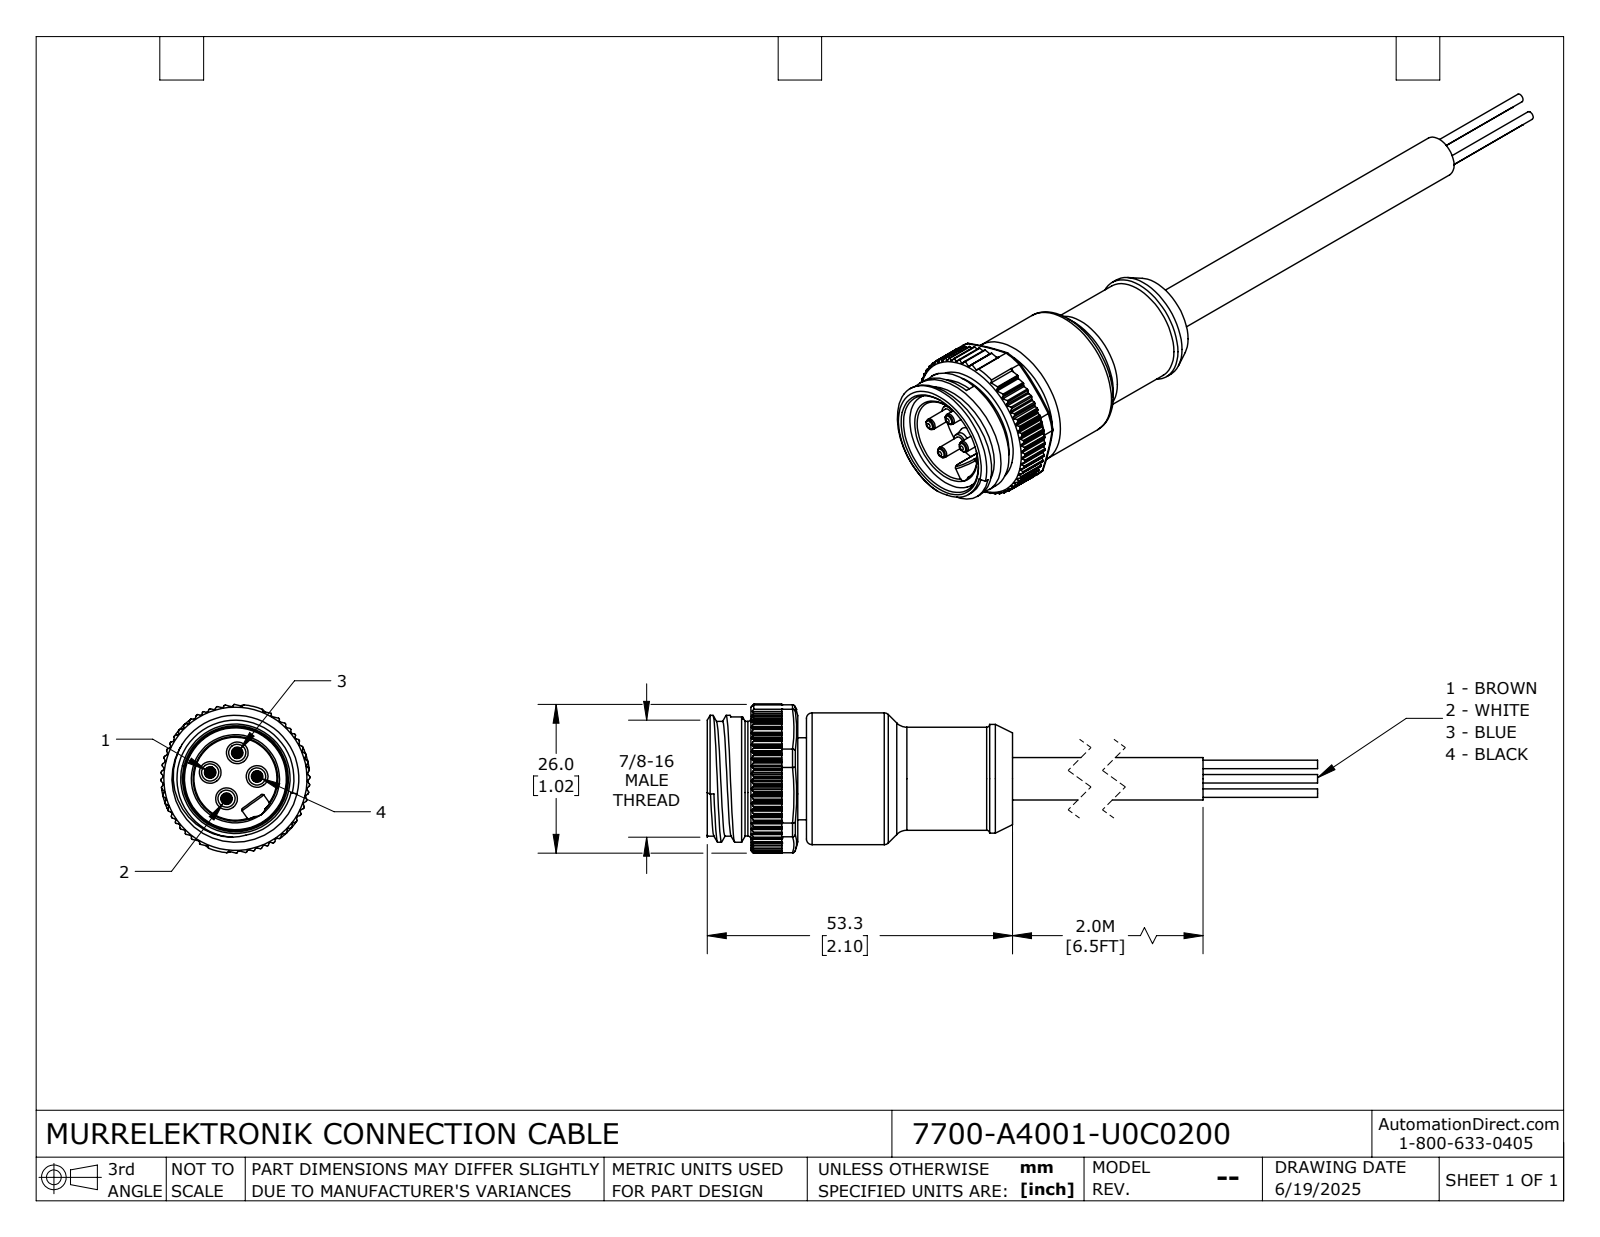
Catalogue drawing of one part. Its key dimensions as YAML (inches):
part_name: "7700-A4001-U0C0200"
step_written_by: "SolidWorks 2024 (CONFIG_CONTROL_DESIGN)"
units: inches
bodies: {solids: 1, faces: 580, planar: 236, cylindrical: 266, other: 78}
overall_size: [5.642, 1.024, 1.024]
volume: 1.227
surface_area: 14.39
round_holes:
  - {diameter: 0.614, count: 1}
  - {diameter: 0.728, count: 1}
round_bosses_or_shafts:
  - {diameter: 0.118, count: 4}
  - {diameter: 0.079, count: 4}
  - {diameter: 0.059, count: 4}
  - {diameter: 0.906, count: 1}
  - {diameter: 0.873, count: 1}
  - {diameter: 0.789, count: 1}
  - {diameter: 0.787, count: 1}
  - {diameter: 0.748, count: 1}
partial_cylinders:
  - {radius: 0.008, count: 126}
  - {radius: 0.012, count: 18}
  - {radius: 0.004, count: 4}
  - {radius: 0.028, count: 4}
  - {radius: 0.093, count: 1}
  - {radius: 0.512, count: 1}
face_to_face_distances: [0.059, 1.476, 1.417, 0.323, 0.382, 1.799, 0.035, 0.287, 0.346, 1.764]
